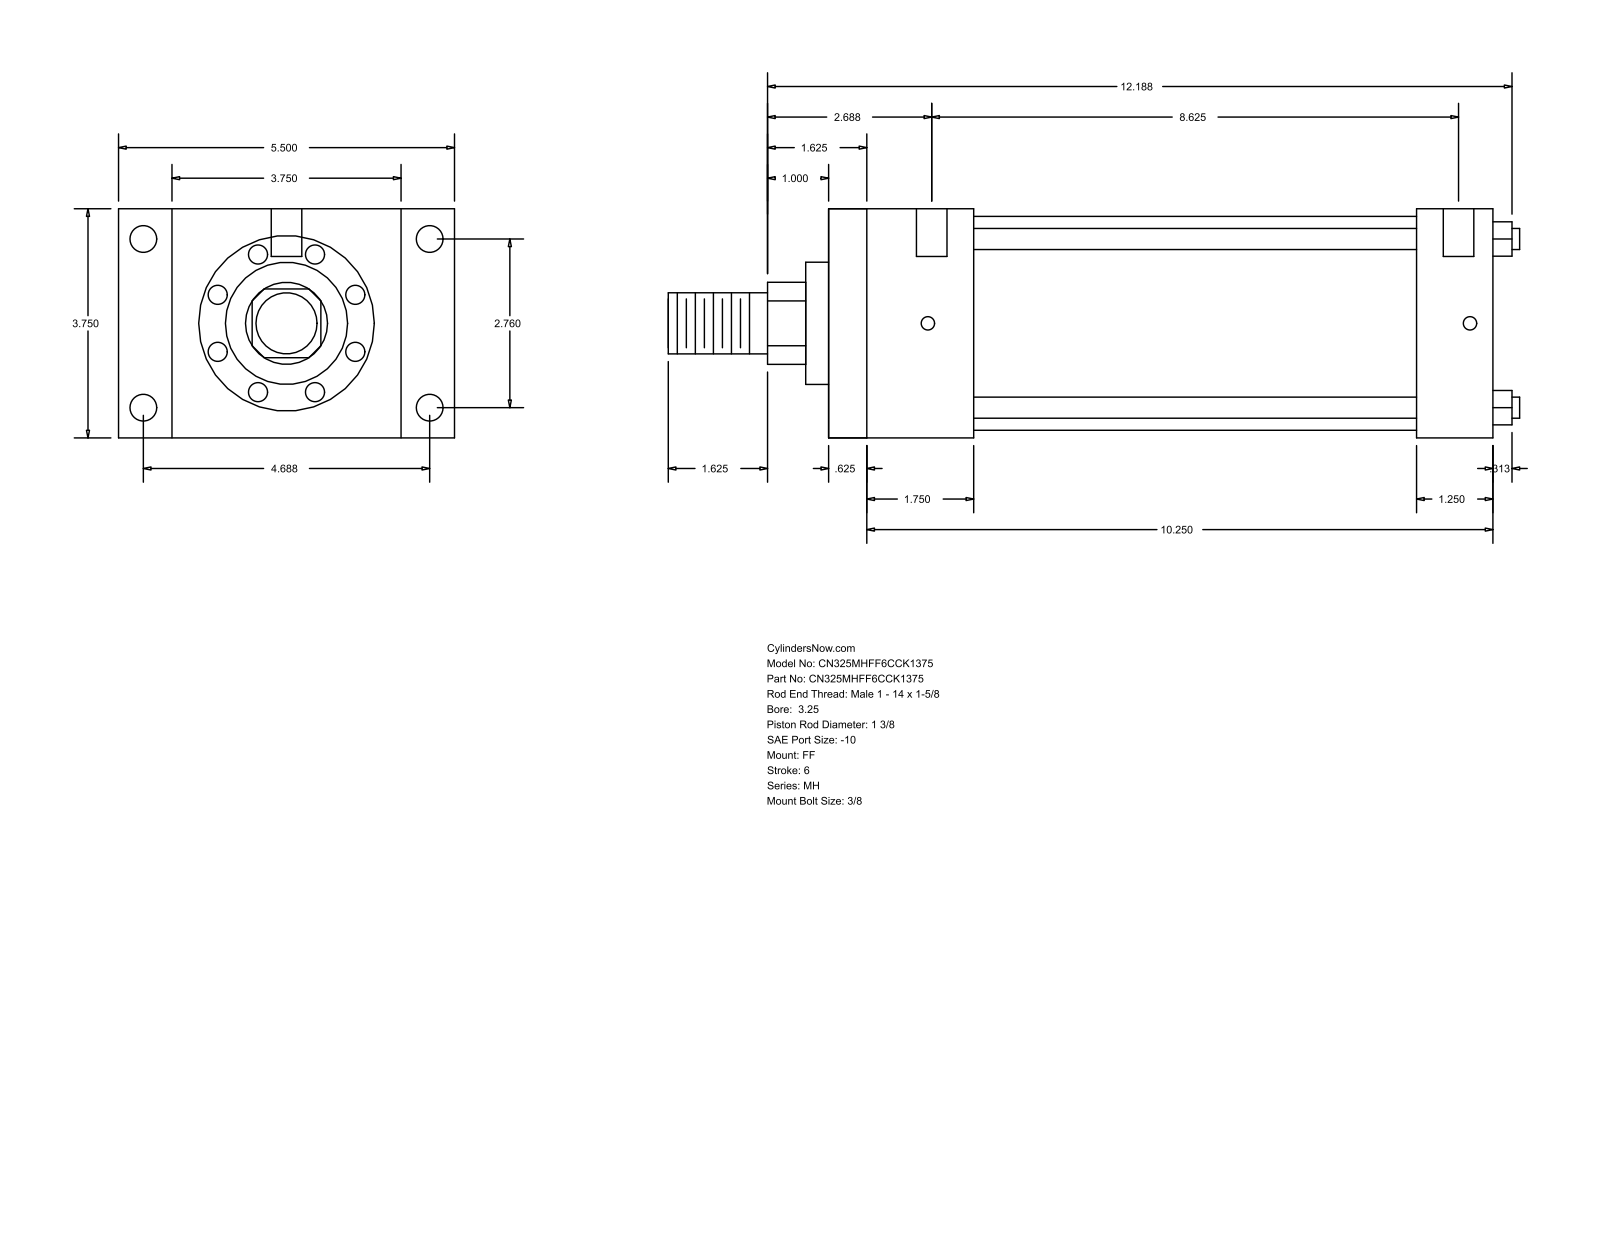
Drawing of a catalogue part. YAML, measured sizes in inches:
part_name: "MH_FF__0325_1.375"
step_written_by: "GSSL Pune (CONFIG_CONTROL_DESIGN)"
units: inches
bodies: {solids: 0, faces: 92, planar: 64, cylindrical: 28, other: 0}
overall_size: [13.937, 5.5, 3.75]
round_holes:
  - {diameter: 0.219, count: 4}
  - {diameter: 0.438, count: 4}
  - {diameter: 0.5, count: 2}
round_bosses_or_shafts:
  - {diameter: 0.345, count: 4}
  - {diameter: 3.5, count: 1}
  - {diameter: 2, count: 1}
  - {diameter: 1.375, count: 1}
  - {diameter: 1, count: 1}
partial_cylinders:
  - {radius: 0.672, count: 1}
face_to_face_distances: [3.75, 10.875, 0.625, 10.25, 0.875, 4.625, 9.625, 9, 1.25, 2.375]
hole_center_spacings: [2.76, 4.687, 5.439, 8.875, 0.063, 0.187, 8.625, 8.688]
